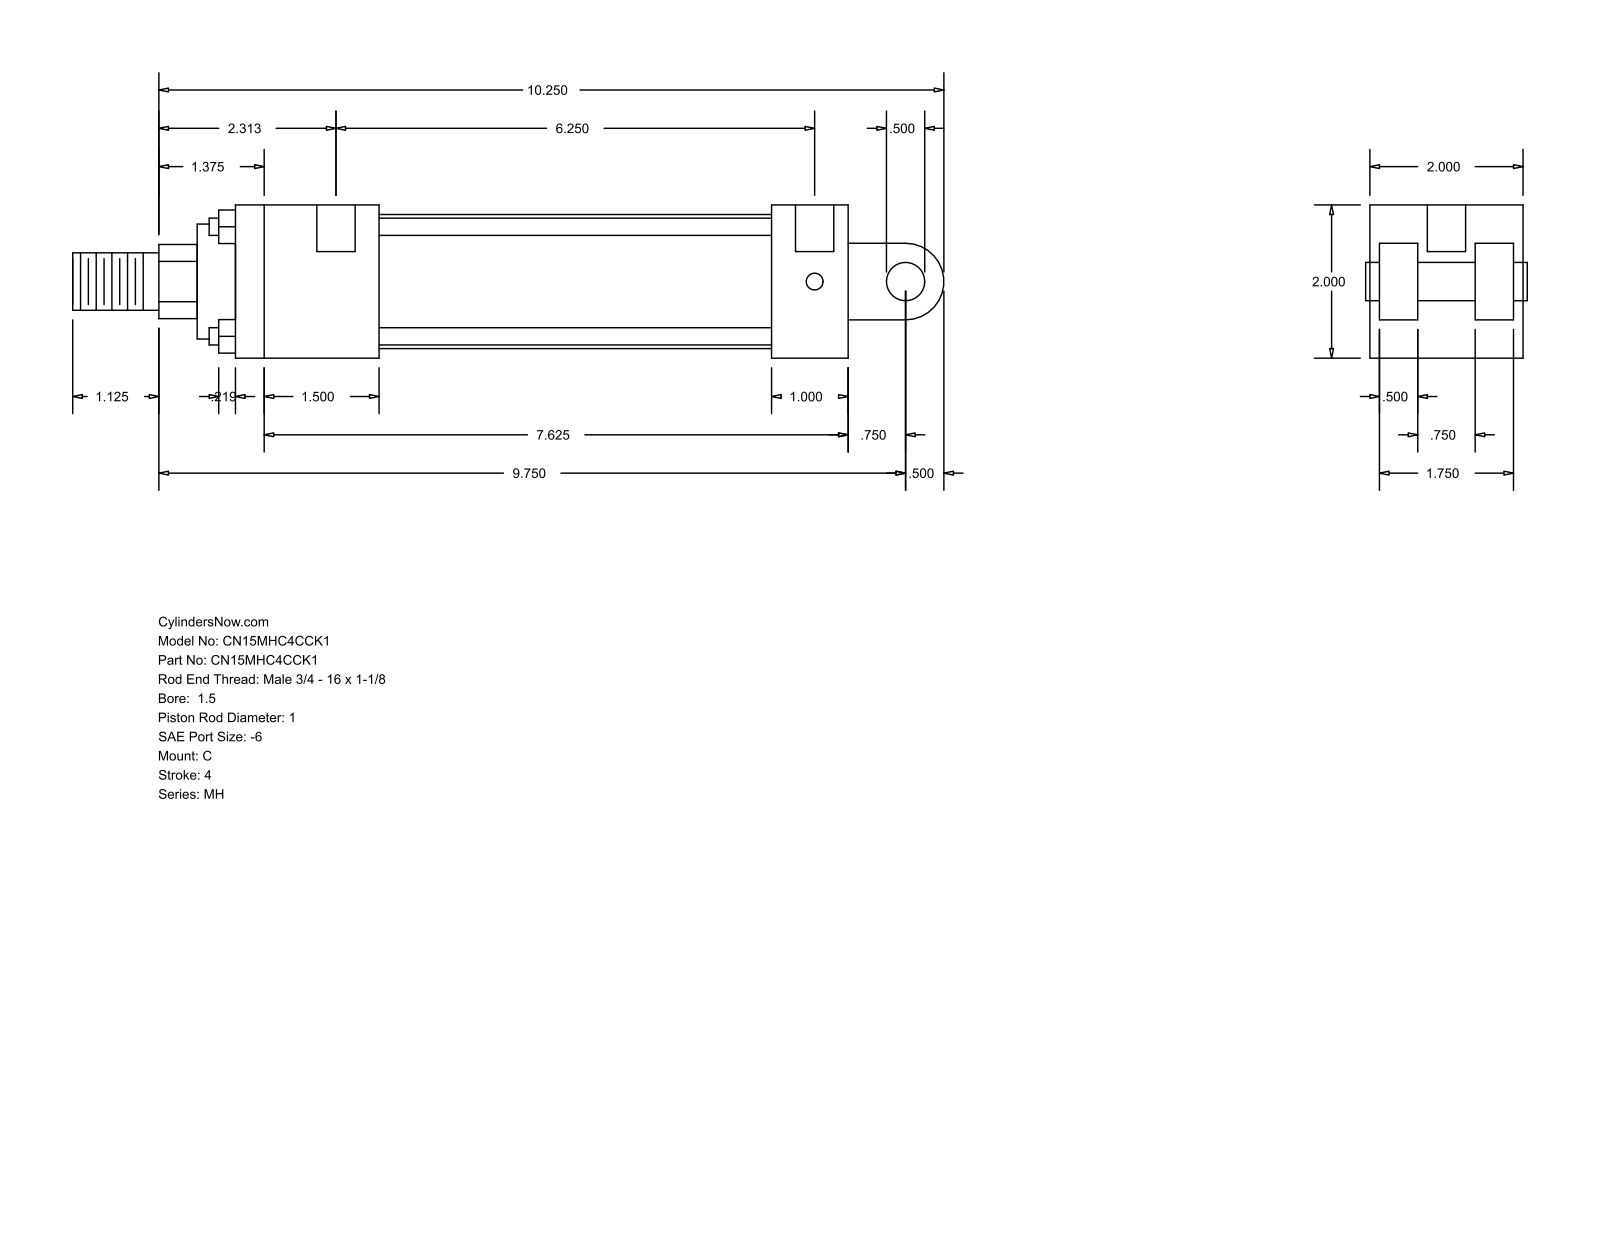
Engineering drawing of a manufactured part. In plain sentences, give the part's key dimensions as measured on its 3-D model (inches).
The part is named "MH_C__0150_1". Its 3-D file was written by "GSSL Pune (CONFIG_CONTROL_DESIGN)". It is 0 solids with 99 faces: 70 planar, 29 cylindrical and 0 other. Overall it measures 11.375 by 2 by 2 inches. Round holes: 4 of diameter 0.219, 2 of diameter 0.5. Round bosses or shafts: 4 of diameter 0.225, 1 of diameter 1.75, 1 of diameter 1.5, 1 of diameter 1, 1 of diameter 0.75, 1 of diameter 0.5. Partial cylindrical surfaces (rounded edges, fillets, slot ends): 1 of radius 0.484, 1 of radius 0.5. The main face-to-face distances are 2, 0.5, 1.875, 1, 0.125, 0.625, 1.375, 1.25, 8, 1.5. The hole center spacings are 6.375, 0.125, 6.25.
